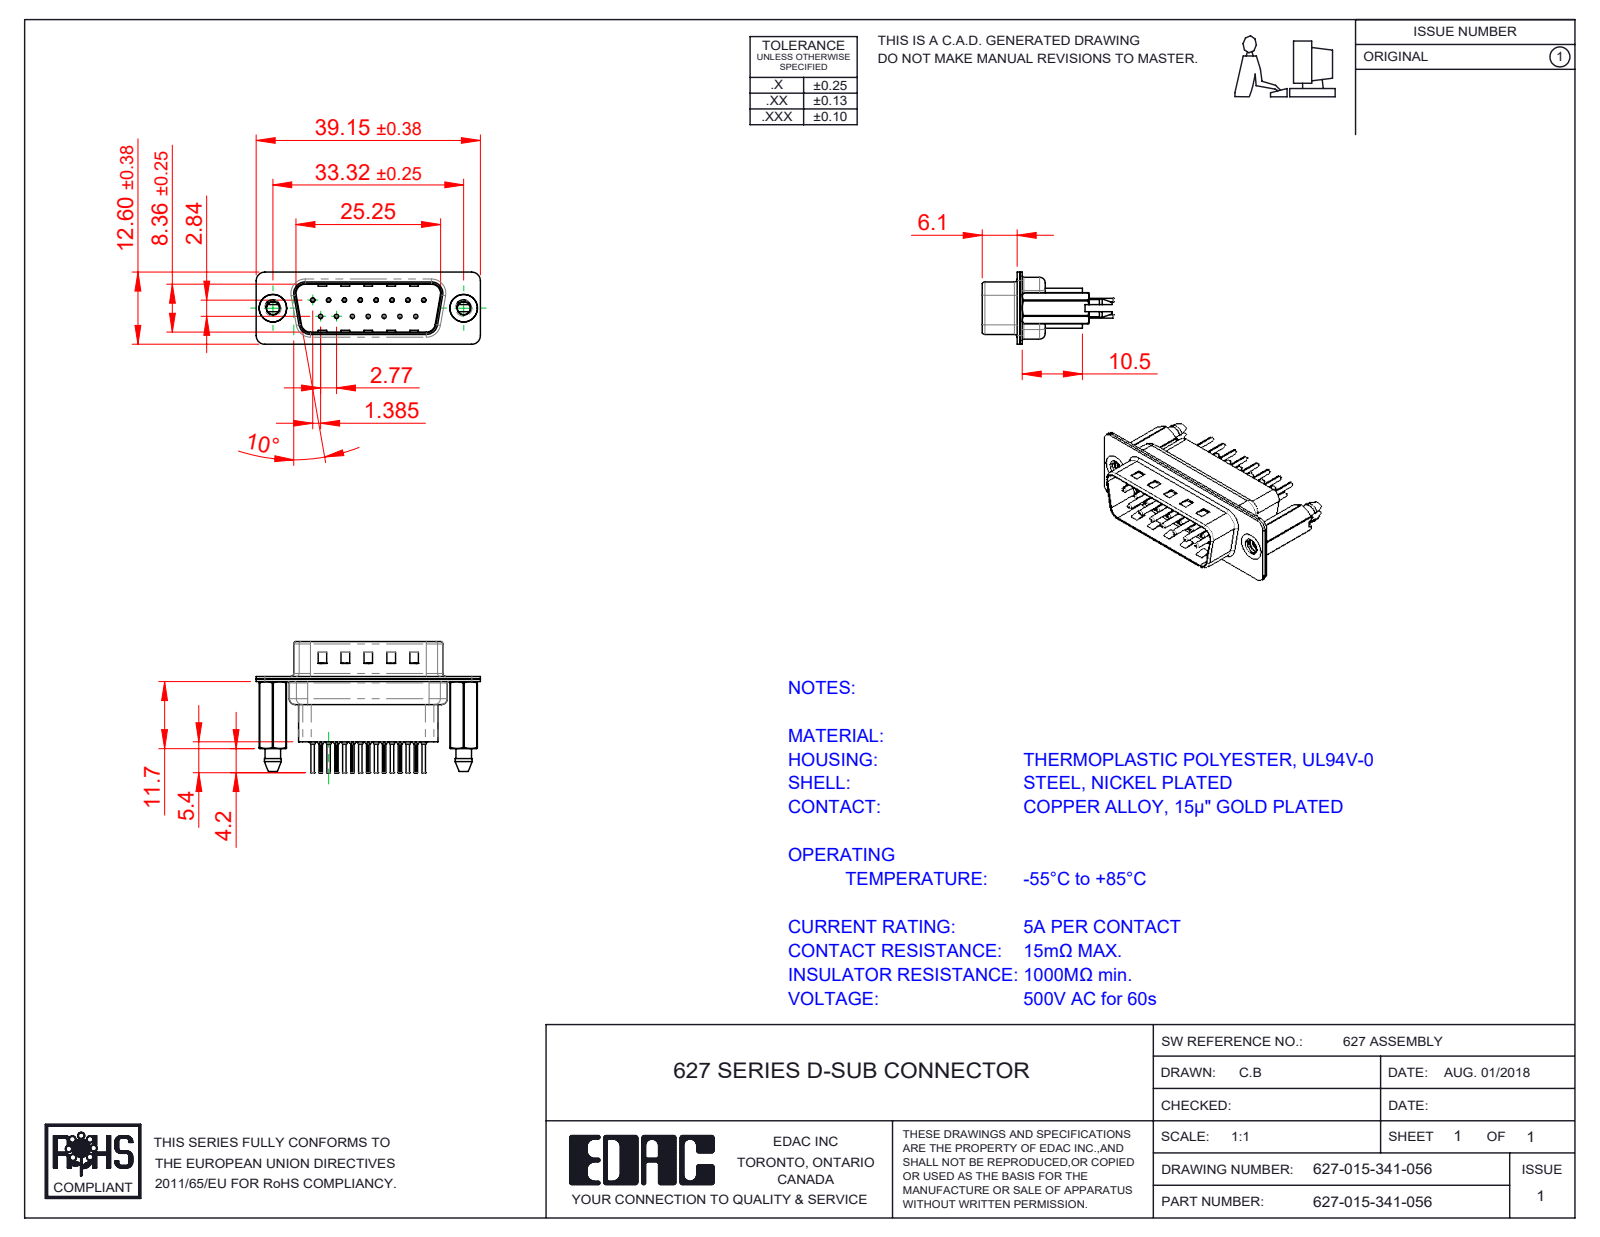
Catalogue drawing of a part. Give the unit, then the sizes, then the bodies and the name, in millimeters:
Units: millimetres
Overall size (bounding box): 39.15 × 22.8 × 12.6
Round holes (diameter × count): ⌀0.2 ×15, ⌀0.35 ×15, ⌀1.1 ×15, ⌀1.6 ×15, ⌀2.26 ×2, ⌀4 ×2, ⌀4.8 ×2
Round bosses / shafts (diameter × count): ⌀2 ×15, ⌀1.5 ×15, ⌀0.75 ×15, ⌀0.6 ×15, ⌀4.9 ×2
Partial cylindrical surfaces — rounded edges, fillets, slot ends (radius × count): R0.1 ×30, R1.5 ×18, R2 ×12, R1.6 ×10, R0.5 ×8, R0.25 ×4, R0.6 ×4, R0.65 ×4
Main face-to-face distances: 0.4, 0.45, 0.9, 0.82, 9.58, 1.5, 0.68, 7.68, 1.4, 1.08
Hole centre spacings: 3.16, 2.77, 5.54, 8.31, 11.08, 5.03, 5.04, 7.48
Volume: 2 826 mm³ · Surface area: 7 322 mm²
Bodies: 20 solids, 1918 faces (531 planar, 754 cylindrical, 633 other)
Part name (STEP PRODUCT): 627-015-341-056; 627 Shell Rear_15 Contacts; 627 Housing_15 HP; 627 Contact Row 1_41 (+3 more)
STEP written by: SolidWorks 2020 (CONFIG_CONTROL_DESIGN)
